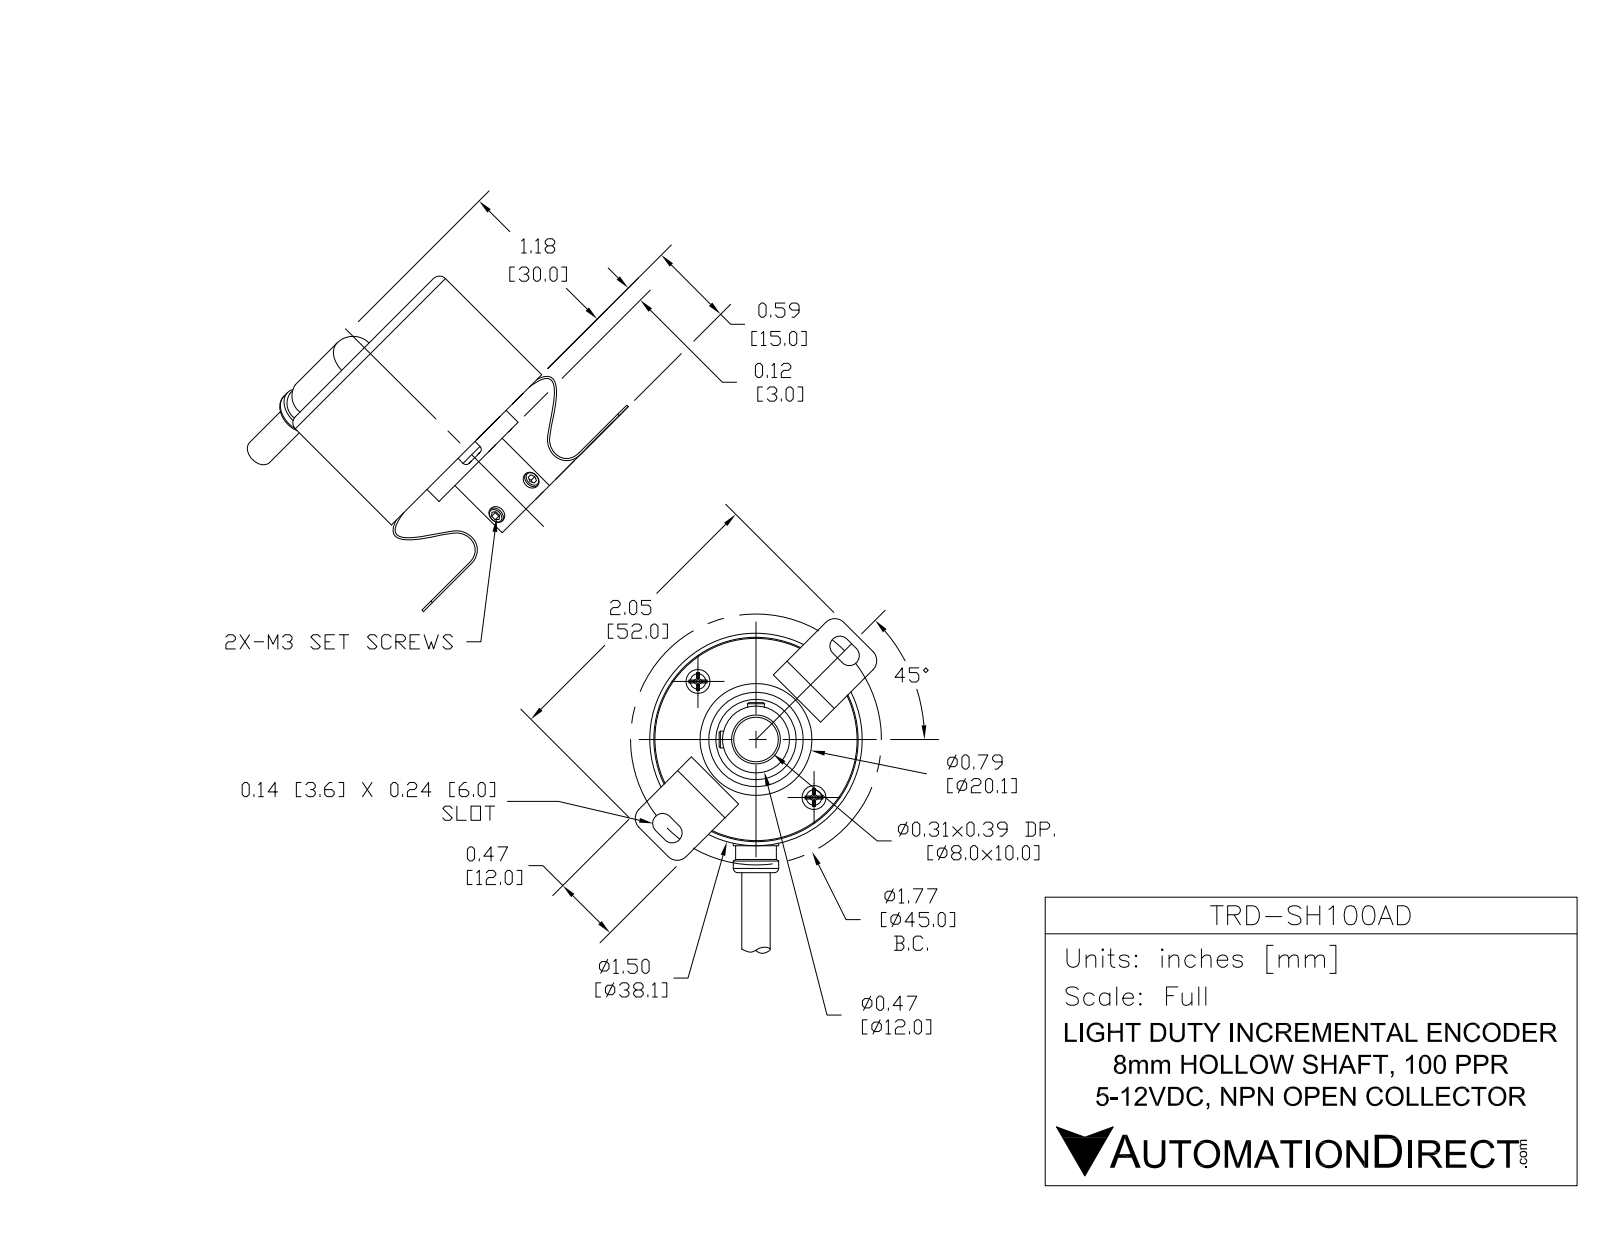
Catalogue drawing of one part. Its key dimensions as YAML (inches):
part_name: "TRD-SH-100"
step_written_by: "SolidWorks 2016 (AUTOMOTIVE_DESIGN)"
units: inches
bodies: {solids: 11, faces: 322, planar: 169, cylindrical: 101, other: 52}
overall_size: [3.952, 1.772, 1.684]
volume: 2.043
surface_area: 17.32
round_holes:
  - {diameter: 0.126, count: 5}
  - {diameter: 0.098, count: 2}
  - {diameter: 0.315, count: 1}
  - {diameter: 0.791, count: 1}
round_bosses_or_shafts:
  - {diameter: 0.118, count: 5}
  - {diameter: 1.496, count: 1}
  - {diameter: 0.787, count: 1}
  - {diameter: 0.591, count: 1}
  - {diameter: 0.472, count: 1}
  - {diameter: 0.299, count: 1}
  - {diameter: 0.197, count: 1}
  - {diameter: 0.134, count: 1}
partial_cylinders:
  - {radius: 0.039, count: 6}
  - {radius: 0.118, count: 5}
  - {radius: 0.03, count: 4}
  - {radius: 0.071, count: 4}
  - {radius: 0.087, count: 4}
  - {radius: 0.098, count: 4}
  - {radius: 0.031, count: 2}
  - {radius: 0.146, count: 2}
face_to_face_distances: [1.024, 0.579, 1.035, 0.591, 1.614, 1.602, 0.567, 0.118, 1.142, 0.106]
hole_center_spacings: [0.551, 0.78, 0.955, 0.285, 0.285, 0.954, 1.065, 1.065]
